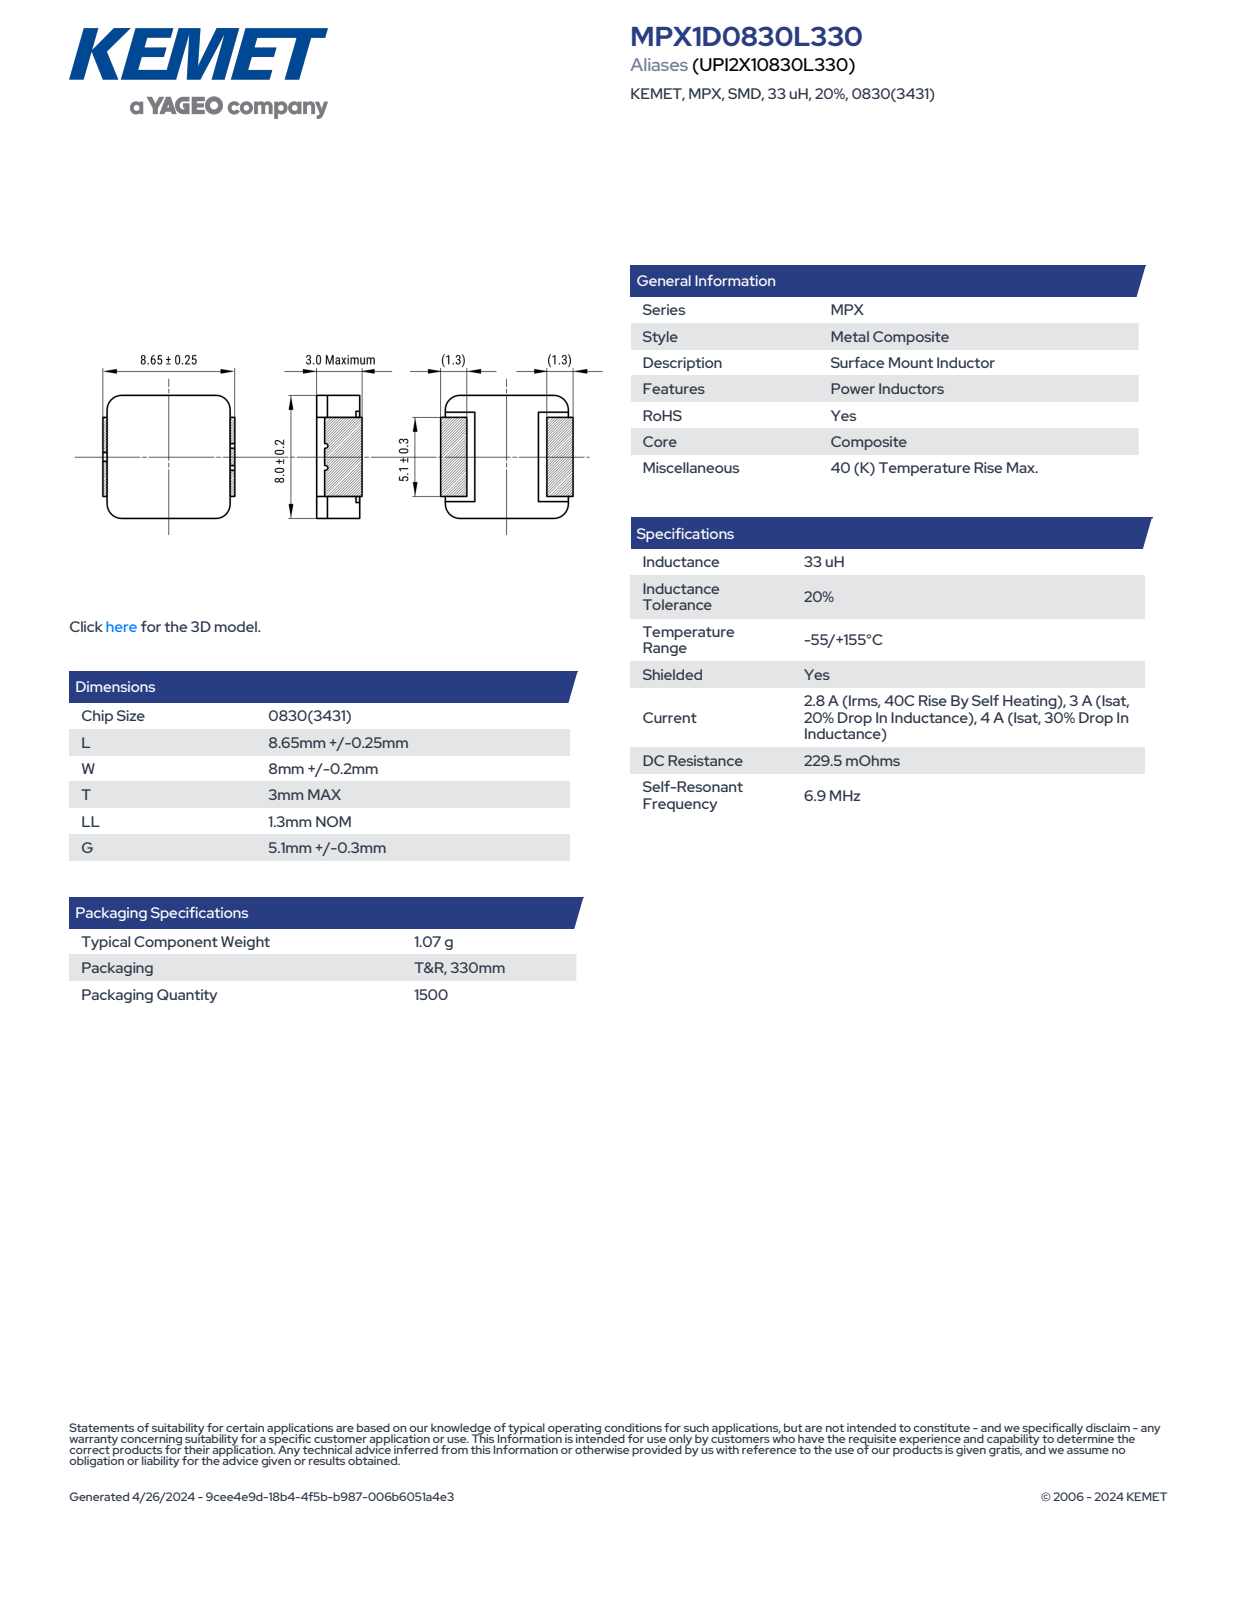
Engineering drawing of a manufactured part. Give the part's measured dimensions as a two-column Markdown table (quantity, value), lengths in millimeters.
| quantity | value |
| --- | --- |
| part name | MPX0830(KEMET) |
| STEP written by | SolidWorks 2018 (AUTOMOTIVE_DESIGN) |
| units | millimeters |
| bodies | 1 solid, 136 faces (115 planar, 21 cylindrical, 0 other) |
| overall size | 8.9 × 8.2 × 3 |
| volume | 199 mm³ |
| surface area | 282 mm² |
| partial cylindrical surfaces (radius × count) | 0.26 × 4, 0.99 × 4, 1 × 4, 0.15 × 2, 0.3 × 1 |
| main face-to-face distances | 2.94, 8.2, 0.35, 8.29, 8.55, 8.64, 2.74, 3, 8.38, 8.9 |
